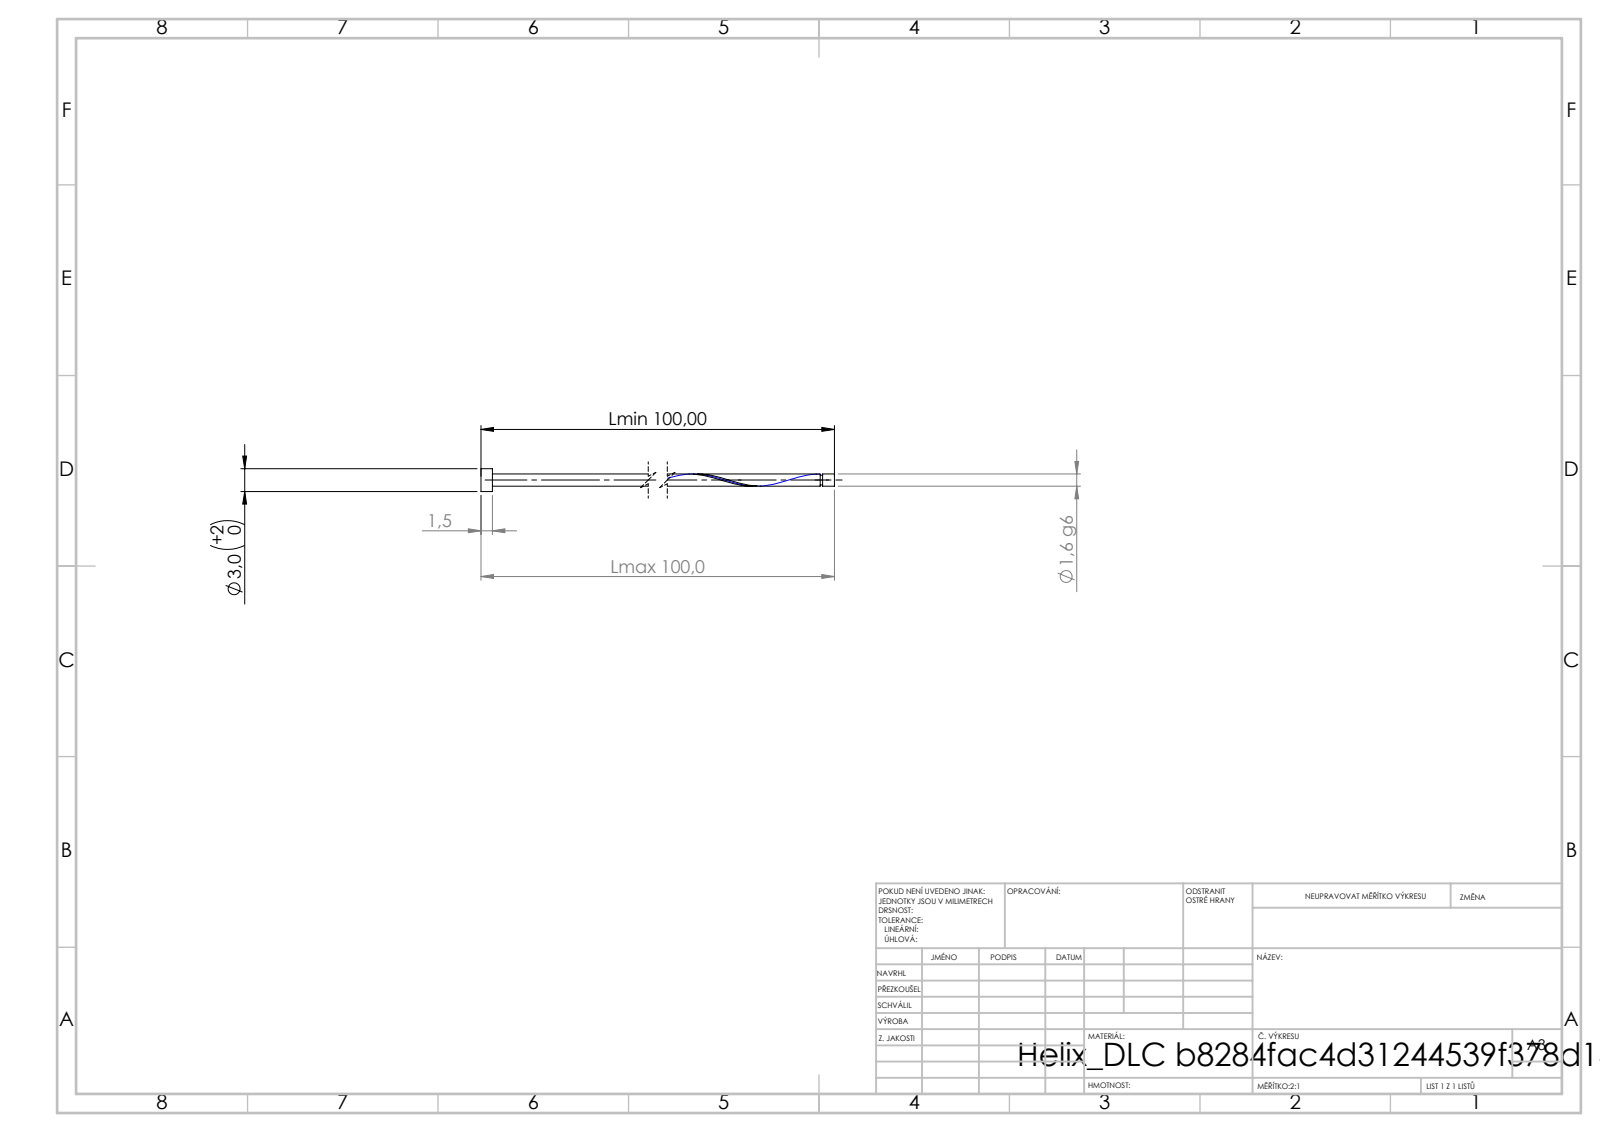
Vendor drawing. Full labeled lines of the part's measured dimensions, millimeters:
STEP written by: SolidWorks 2019 (CONFIG_CONTROL_DESIGN)
Units: millimetres
Bodies: 1 solid, 16 faces (6 planar, 9 cylindrical, 1 other)
Overall size (bounding box): 100 × 3 × 3
Volume: 251 mm³ · Surface area: 700 mm²
Round bosses / shafts (diameter × count): ⌀3 ×1, ⌀1.6 ×1, ⌀1.28 ×1
Main face-to-face distances: 1.5, 100, 98.5, 98.45, 96.95, 1.55, 98.13, 96.63, 0.32, 1.87
